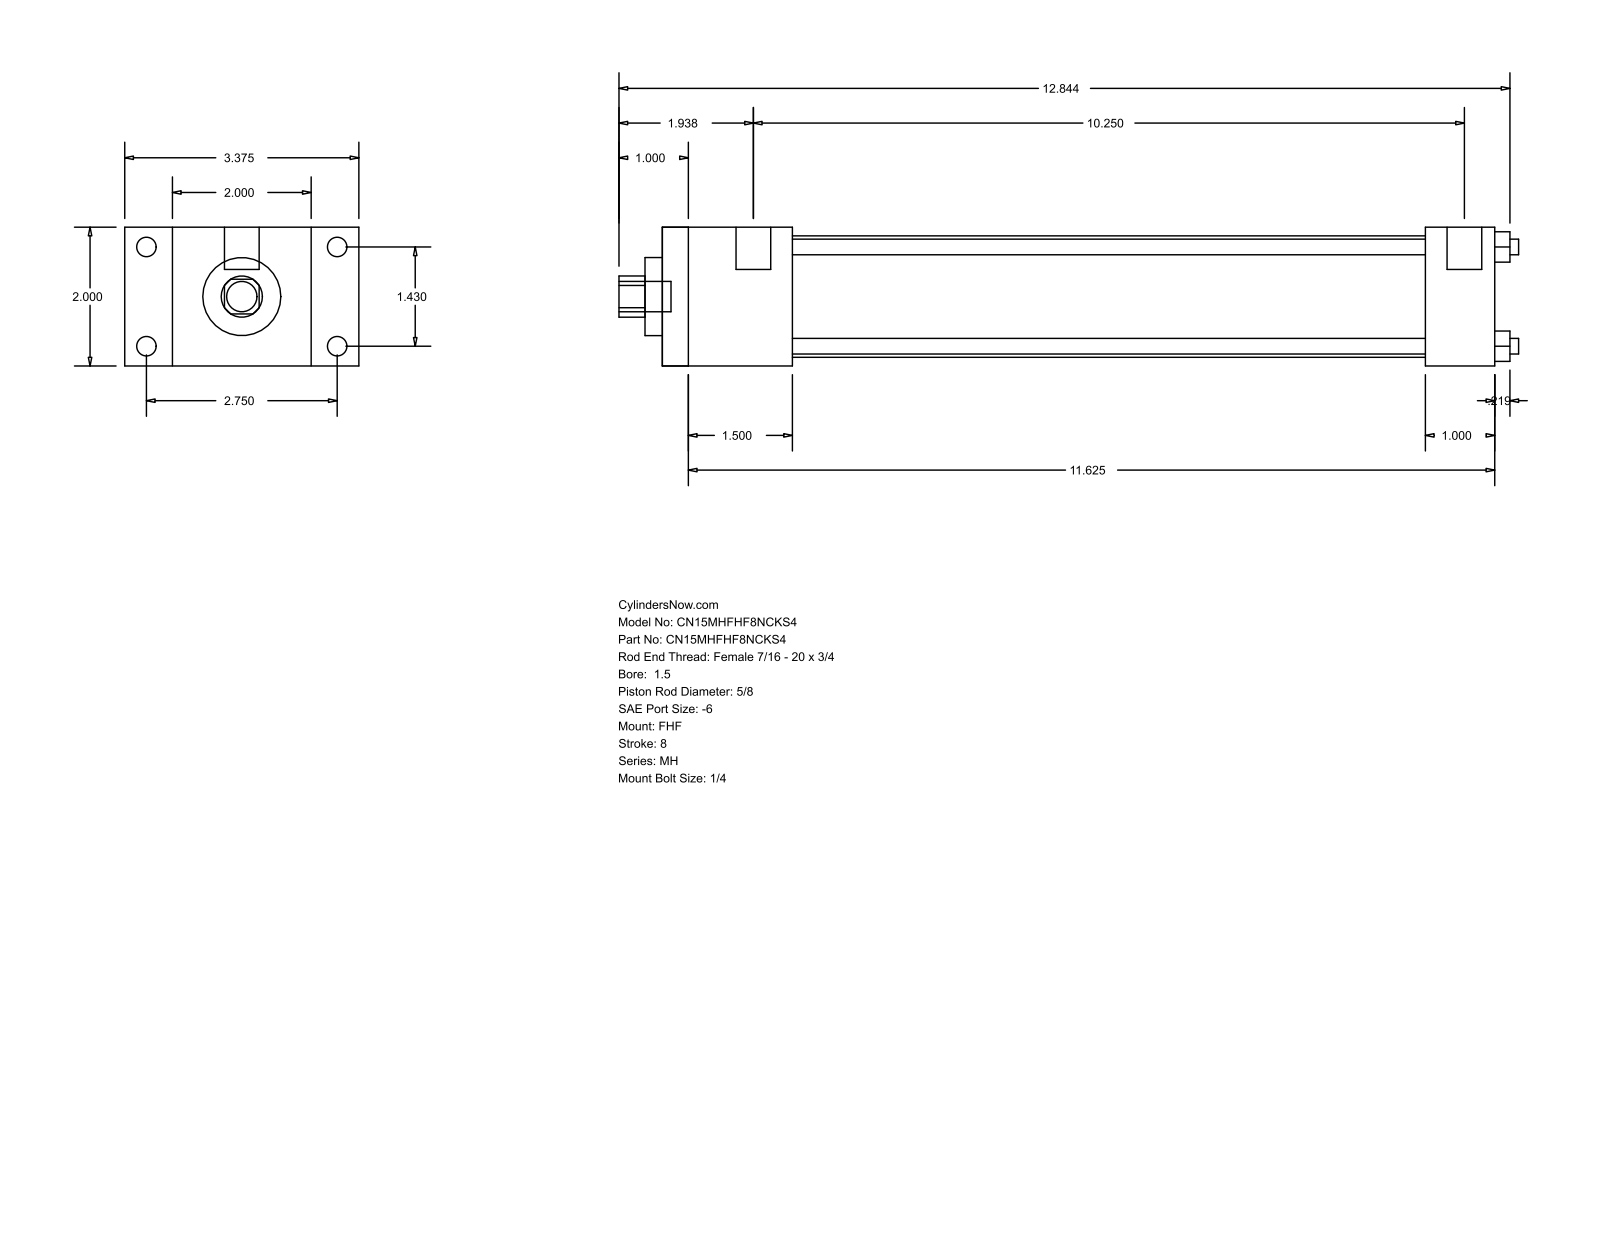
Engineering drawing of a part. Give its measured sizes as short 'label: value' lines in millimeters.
name: MH_FHF__0150_0.625
written by: GSSL Pune (CONFIG_CONTROL_DESIGN)
unit: mm
bodies: 0 solids, 88 faces (60 planar, 28 cylindrical, 0 other)
size: 329.41 × 85.72 × 50.8
holes: 4× ⌀5.71, 1× ⌀15.88, 1× ⌀28.57, 1× ⌀44.45
bosses: 4× ⌀7.14, 4× ⌀5.56, 2× ⌀12.7, 1× ⌀11.11
rounds: 1× R7.54
face distances: 50.8, 17.46, 68.26, 47.62, 85.72, 304.8, 257.18, 279.39, 231.77, 25.41
hole spacings: 25.68, 36.32, 51.36
